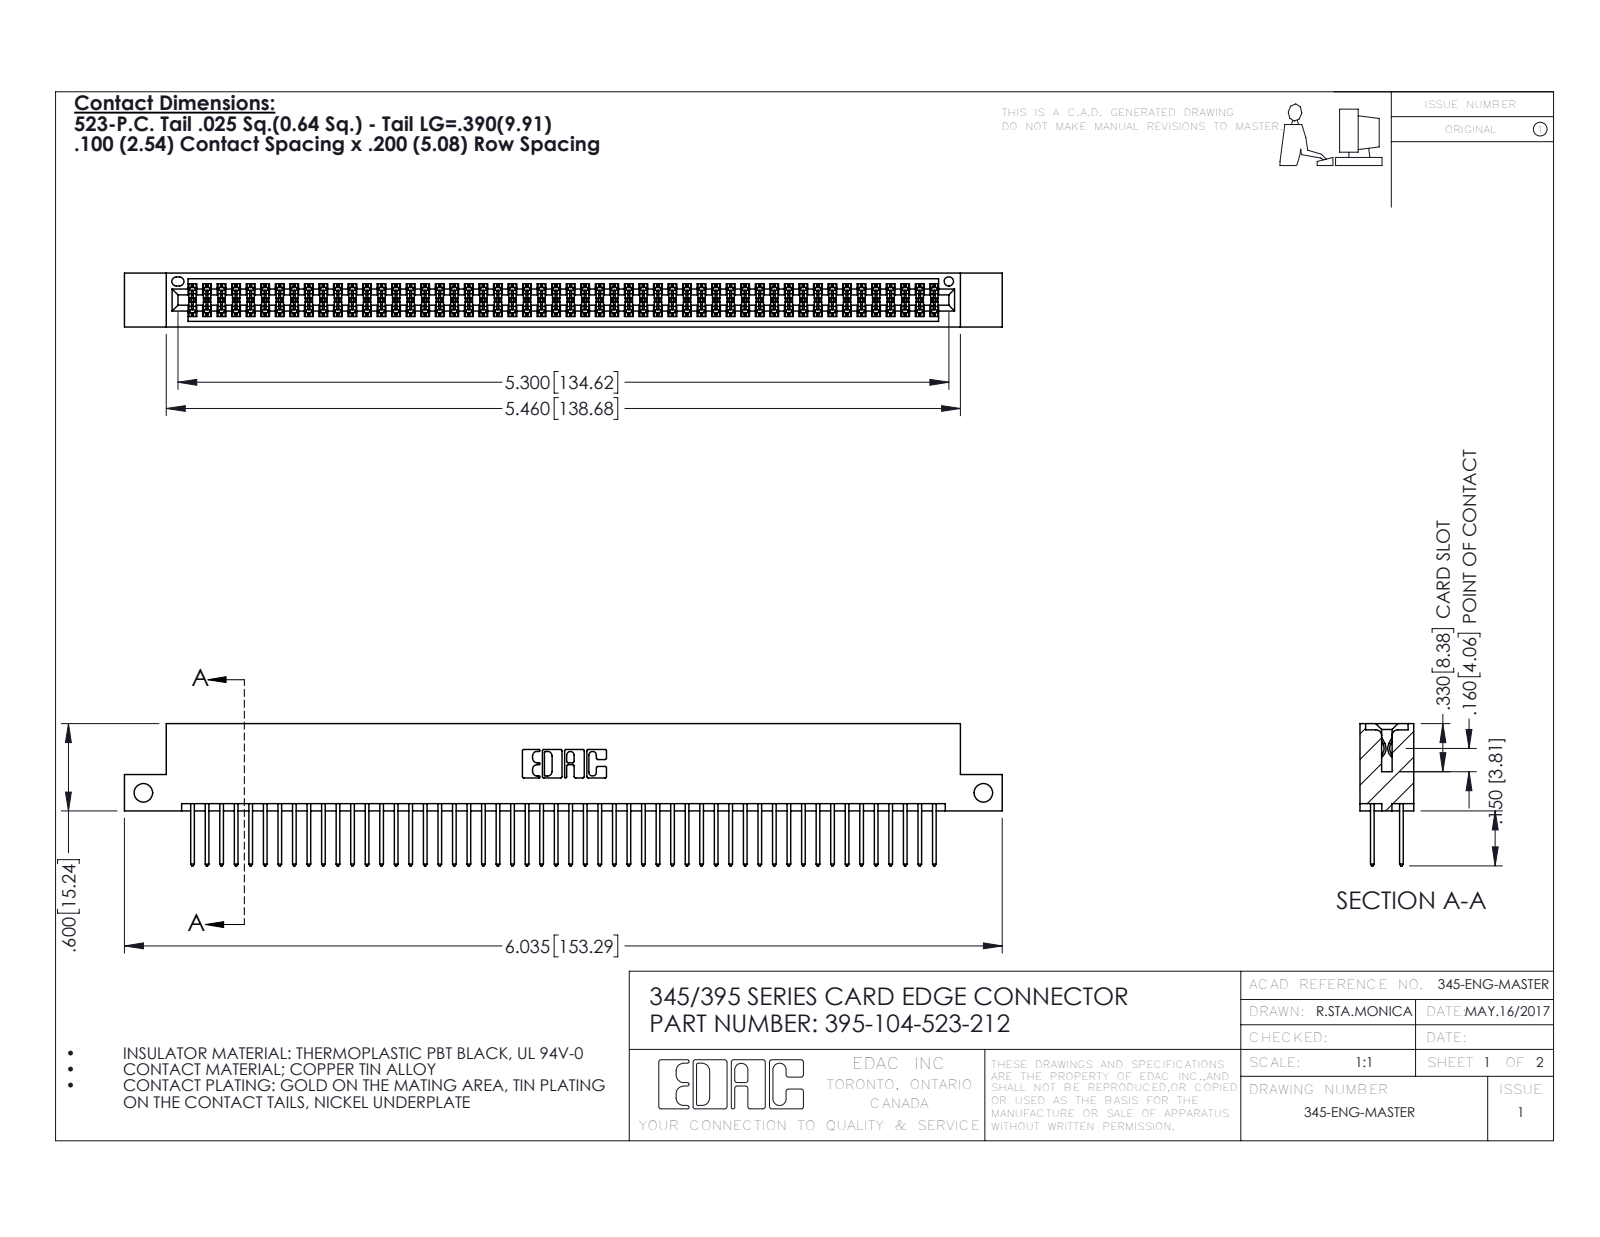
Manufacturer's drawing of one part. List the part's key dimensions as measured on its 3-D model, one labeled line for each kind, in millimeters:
Part name (STEP PRODUCT): 345 Part_Flush Mounting Lugs - Side Mount; 395-104-523-212; 345-292-001_345-293-123
STEP written by: SolidWorks 2016 (CONFIG_CONTROL_DESIGN)
Units: millimetres
Bodies: 105 solids, 5326 faces (3512 planar, 1814 cylindrical, 0 other)
Overall size (bounding box): 153.3 × 24.8 × 9.4
Volume: 15 100 mm³ · Surface area: 23 350 mm²
Round holes (diameter × count): ⌀3.3 ×2, ⌀1.6 ×1
Partial cylindrical surfaces — rounded edges, fillets, slot ends (radius × count): R0.2 ×156, R0.3 ×104, R0.3 ×22, R0.2 ×6, R0.8 ×6, R0.7 ×3, R0.4 ×2, R0.5 ×2
Main face-to-face distances: 7.6, 1.8, 5.1, 2.5, 6.9, 0.6, 9.4, 5.7, 4.4, 3.8
Hole centre spacings: 146.7
